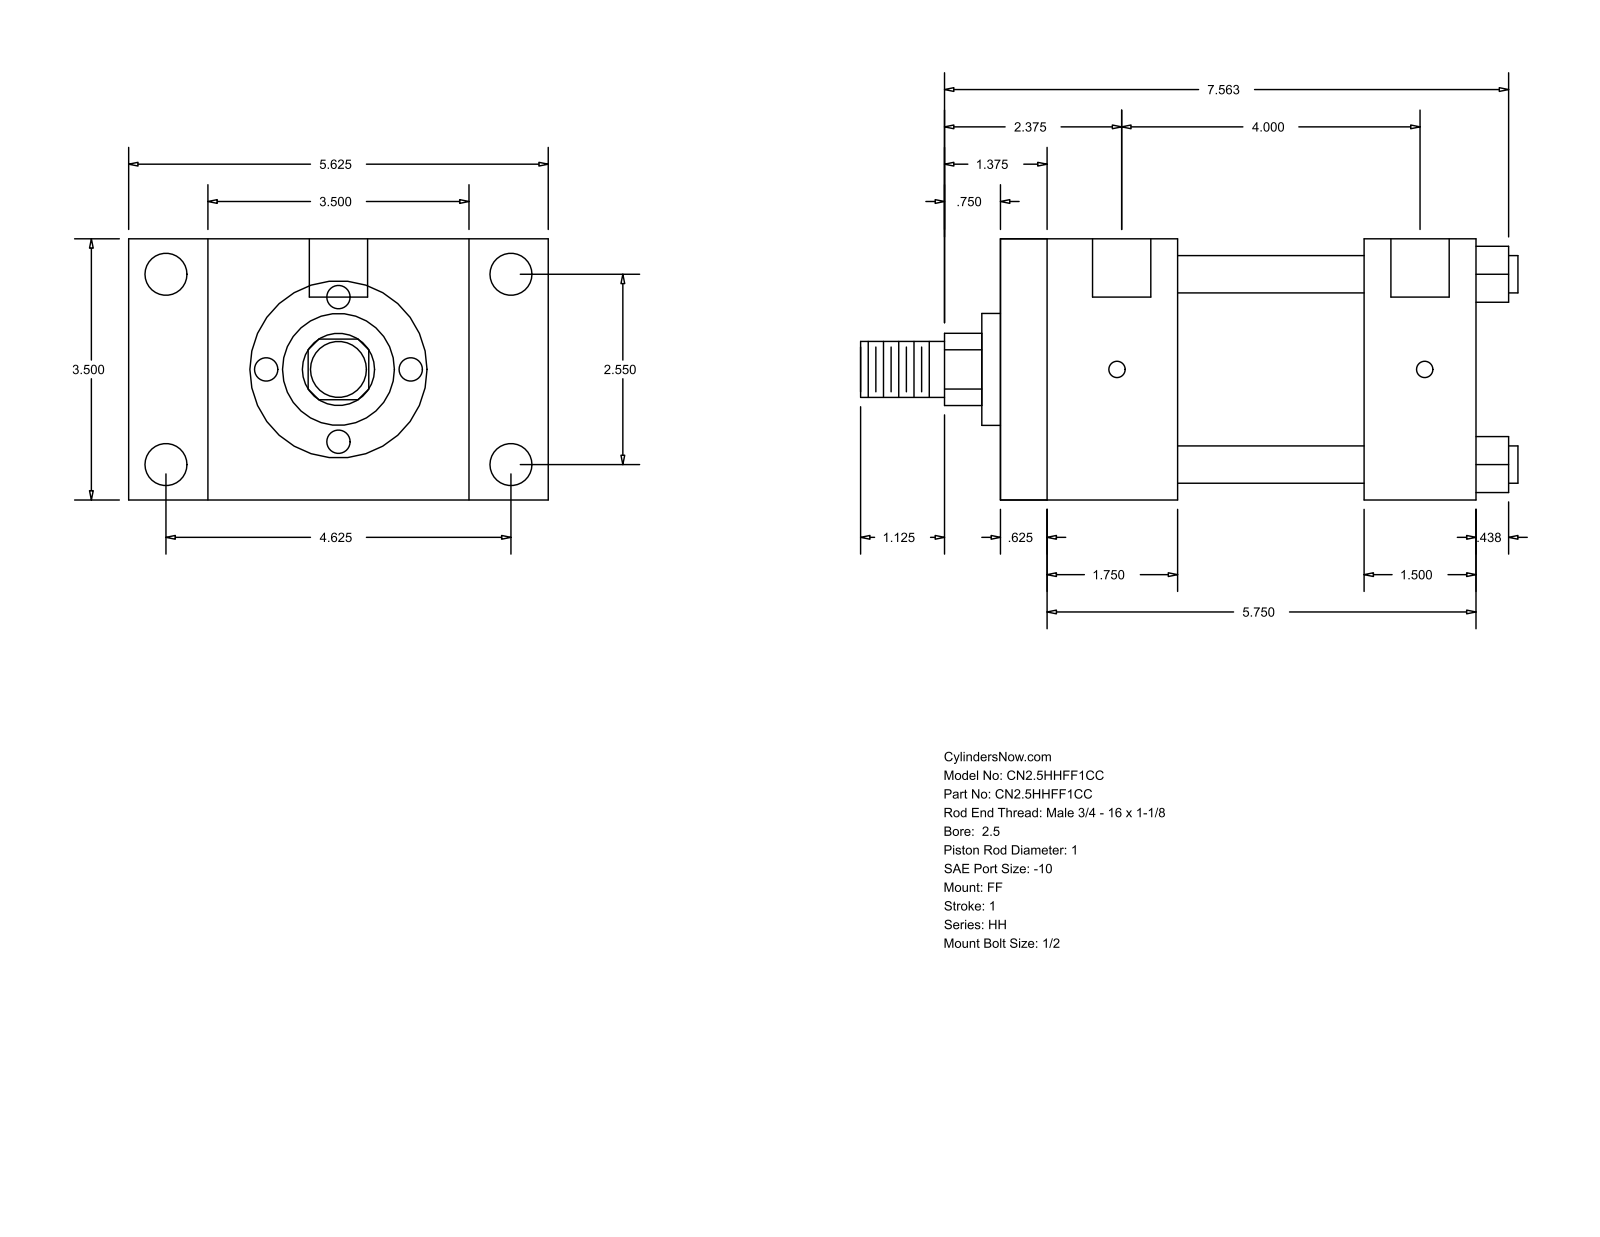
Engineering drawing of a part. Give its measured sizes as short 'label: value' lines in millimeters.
name: HH_FF__0250_1
written by: GSSL Pune (CONFIG_CONTROL_DESIGN)
unit: mm
bodies: 0 solids, 92 faces (64 planar, 28 cylindrical, 0 other)
size: 223.84 × 142.88 × 88.9
holes: 4× ⌀5.56, 4× ⌀14.3, 2× ⌀19.84
bosses: 4× ⌀12.7, 1× ⌀73.03, 1× ⌀38.1, 1× ⌀25.4, 1× ⌀19.05
rounds: 1× R12.29
face distances: 88.9, 161.92, 15.87, 146.05, 60.33, 44.46, 101.59, 123.83, 107.96, 63.5
hole spacings: 64.76, 104.77, 117.48, 134.15, 1.58, 1.59, 101.6, 103.18
